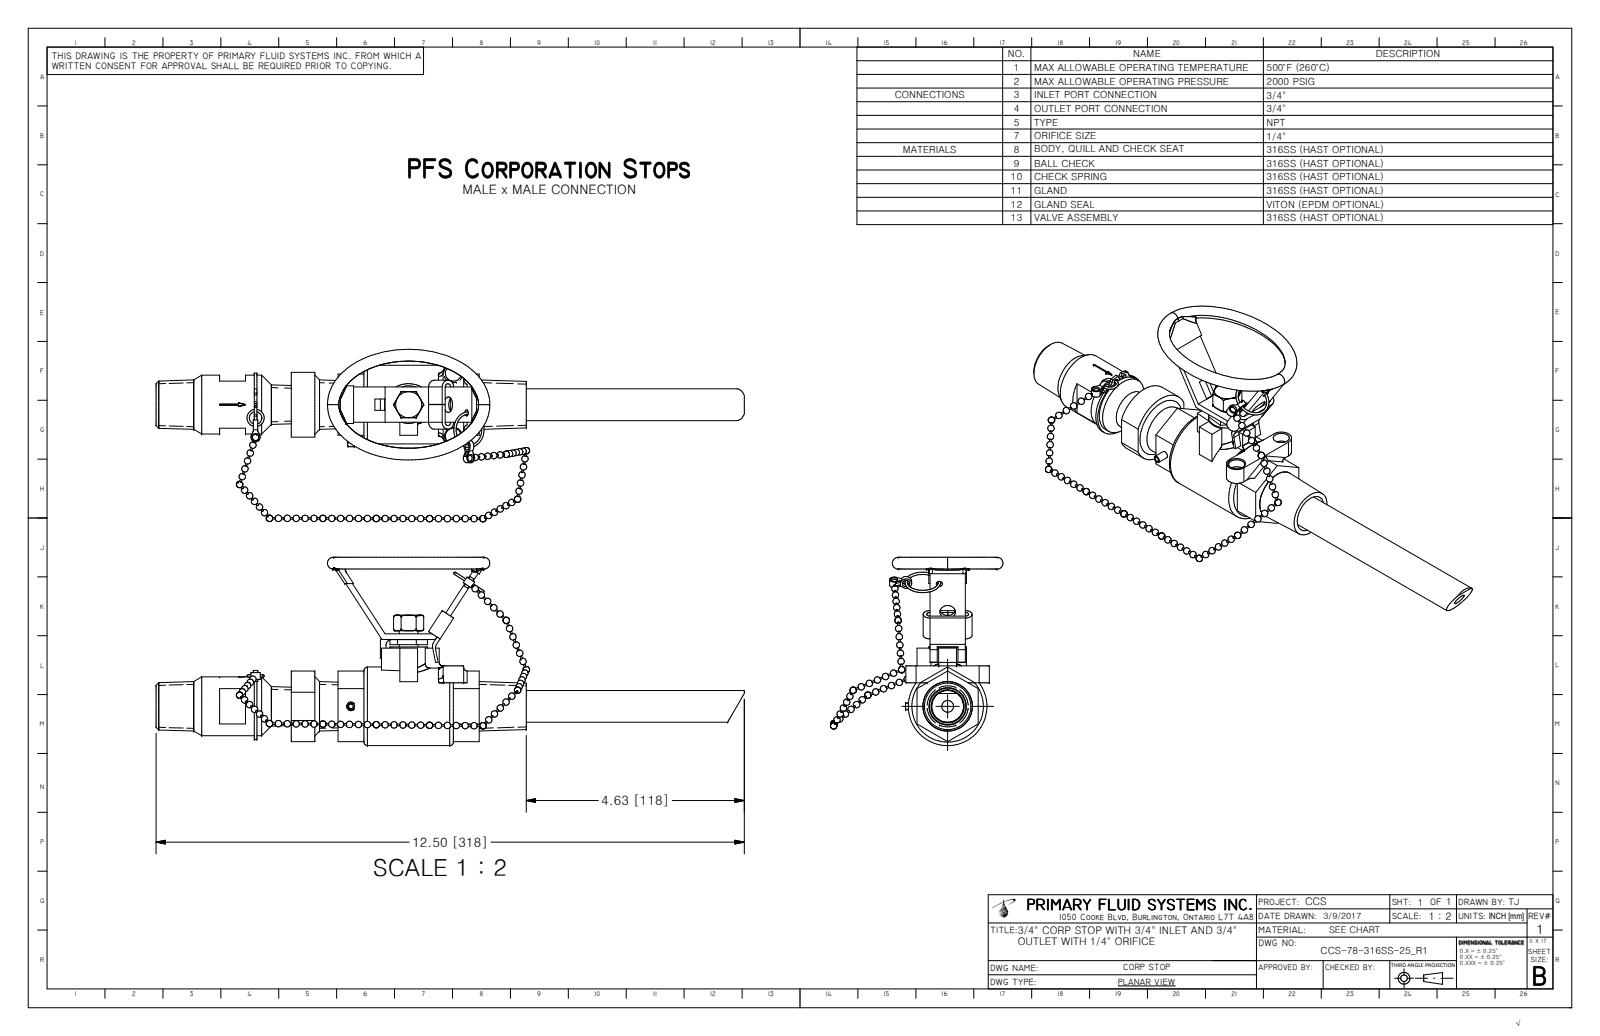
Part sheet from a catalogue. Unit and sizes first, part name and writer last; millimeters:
Units: millimetres
Overall size (bounding box): 317.5 × 101.6 × 93.1
Round holes (diameter × count): ⌀2.5 ×1, ⌀6.4 ×1, ⌀11.9 ×1
Round bosses / shafts (diameter × count): ⌀42.4 ×1, ⌀34.1 ×1, ⌀31.8 ×1, ⌀20.3 ×1, ⌀17.1 ×1, ⌀10.2 ×1, ⌀3.8 ×1
Partial cylindrical surfaces — rounded edges, fillets, slot ends (radius × count): R1.9 ×4, R1.3 ×2, R1.4 ×2, R3.7 ×2, R3.8 ×2, R5 ×2, R3.2 ×1, R4.2 ×1
Main face-to-face distances: 33, 3, 25.4, 3.8, 29.2, 14, 7, 26, 3.2, 3
Hole centre spacings: 16.7
Bodies: 0 solids, 415 faces (178 planar, 41 cylindrical, 196 other)
Part name (STEP PRODUCT): CCS-78-316SS-25_R0
STEP written by: Autodesk Inventor 2009 (AUTOMOTIVE_DESIGN)
